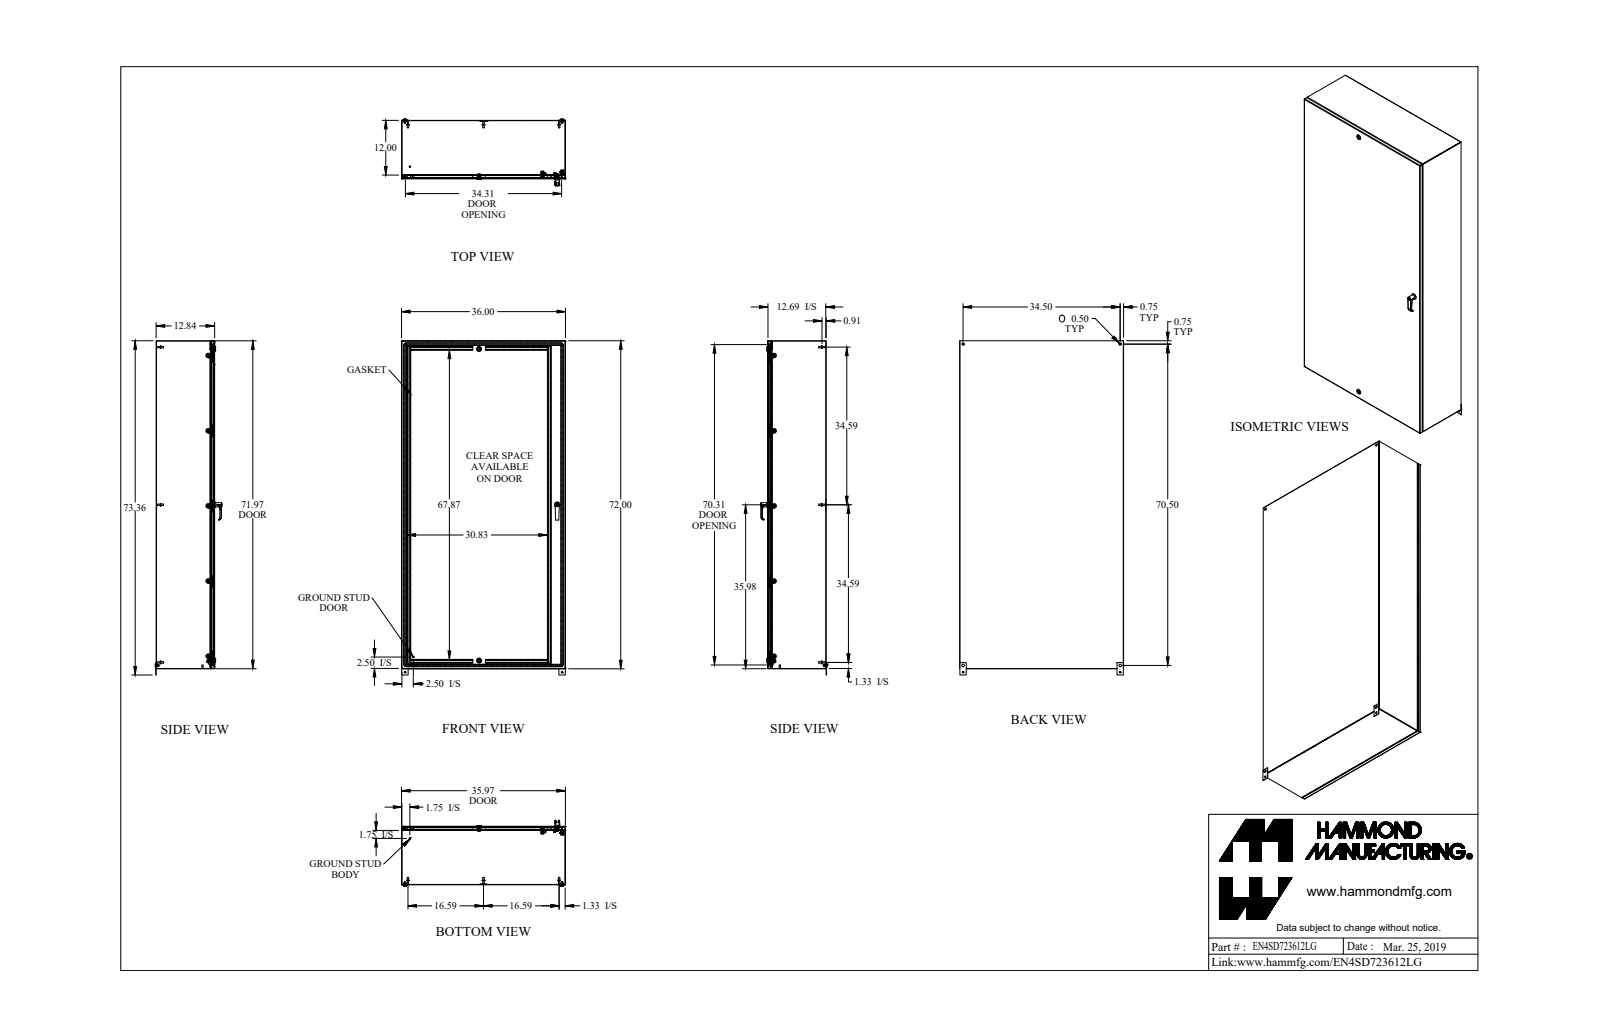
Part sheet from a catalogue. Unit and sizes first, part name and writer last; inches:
Units: inches
Overall size (bounding box): 73.363 × 36 × 14.693
Round holes (diameter × count): ⌀0.176 ×10, ⌀0.196 ×6, ⌀0.25 ×5, ⌀0.265 ×5, ⌀0.413 ×5, ⌀0.256 ×4, ⌀0.313 ×4, ⌀0.39 ×4, ⌀0.394 ×4, ⌀0.5 ×4, ⌀0.232 ×2, ⌀0.307 ×2
Round bosses / shafts (diameter × count): ⌀0.25 ×11, ⌀0.375 ×10, ⌀0.156 ×10, ⌀0.625 ×9, ⌀0.313 ×8, ⌀0.27 ×8, ⌀1 ×5, ⌀0.63 ×4
Partial cylindrical surfaces — rounded edges, fillets, slot ends (radius × count): R0.043 ×24, R0.062 ×19, R0.036 ×17, R0.108 ×17, R0.03 ×15, R0.125 ×14, R0.006 ×10, R0.094 ×10
Main face-to-face distances: 0.072, 12.765, 12.693, 12.837, 35.928, 35.856, 36, 71.928, 71.856, 72
Hole centre spacings: 16.487, 16.513, 33, 49.487, 34.5, 1.5, 2.507, 16.305
Volume: 650.5 in³ · Surface area: 18 283 in²
Bodies: 100 solids, 2461 faces (1167 planar, 902 cylindrical, 392 other)
Part name (STEP PRODUCT): EN4SD723612LG
STEP written by: SolidWorks 2018 (AUTOMOTIVE_DESIGN)
